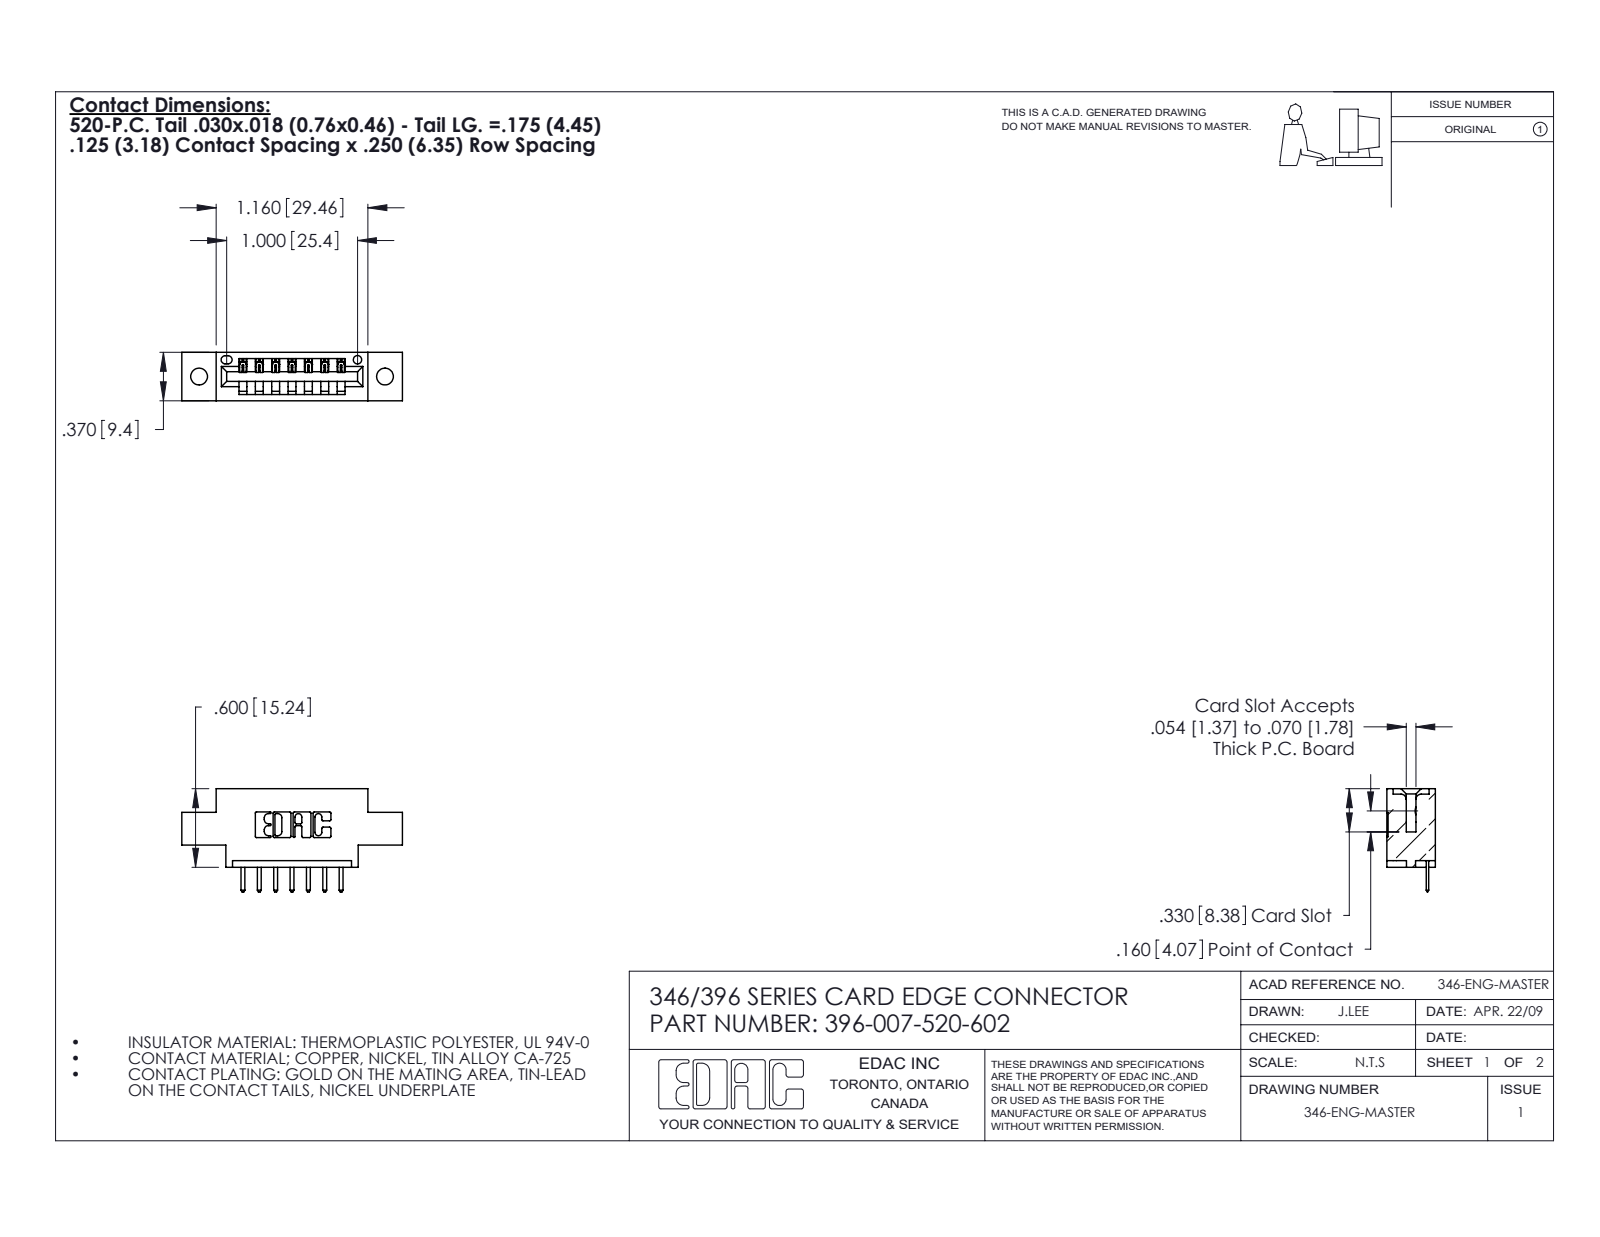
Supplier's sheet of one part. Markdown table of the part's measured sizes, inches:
| quantity | value |
| --- | --- |
| part name | 396-007-520-602; 345-292-001_345-293-120; 346 Part_0.170 Offset - 0.128 Dia |
| STEP written by | SolidWorks 2020 (CONFIG_CONTROL_DESIGN) |
| units | inches |
| bodies | 8 solids, 560 faces (374 planar, 186 cylindrical, 0 other) |
| overall size | 1.685 × 0.788 × 0.37 |
| volume | 0.222 in³ |
| surface area | 6.198 in² |
| round holes (diameter × count) | 0.128 × 2, 0.064 × 1 |
| partial cylindrical surfaces (radius × count) | 0.01 × 22, 0.01 × 16, 0.006 × 14, 0.007 × 6, 0.031 × 6, 0.026 × 3, 0.031 × 2, 0.04 × 2 |
| main face-to-face distances | 0.25, 0.37, 0.048, 0.322, 0.148, 0.222, 0.1, 0.174, 0.125, 0.185 |
| hole center spacings | 0.246, 1.217, 1.42 |
